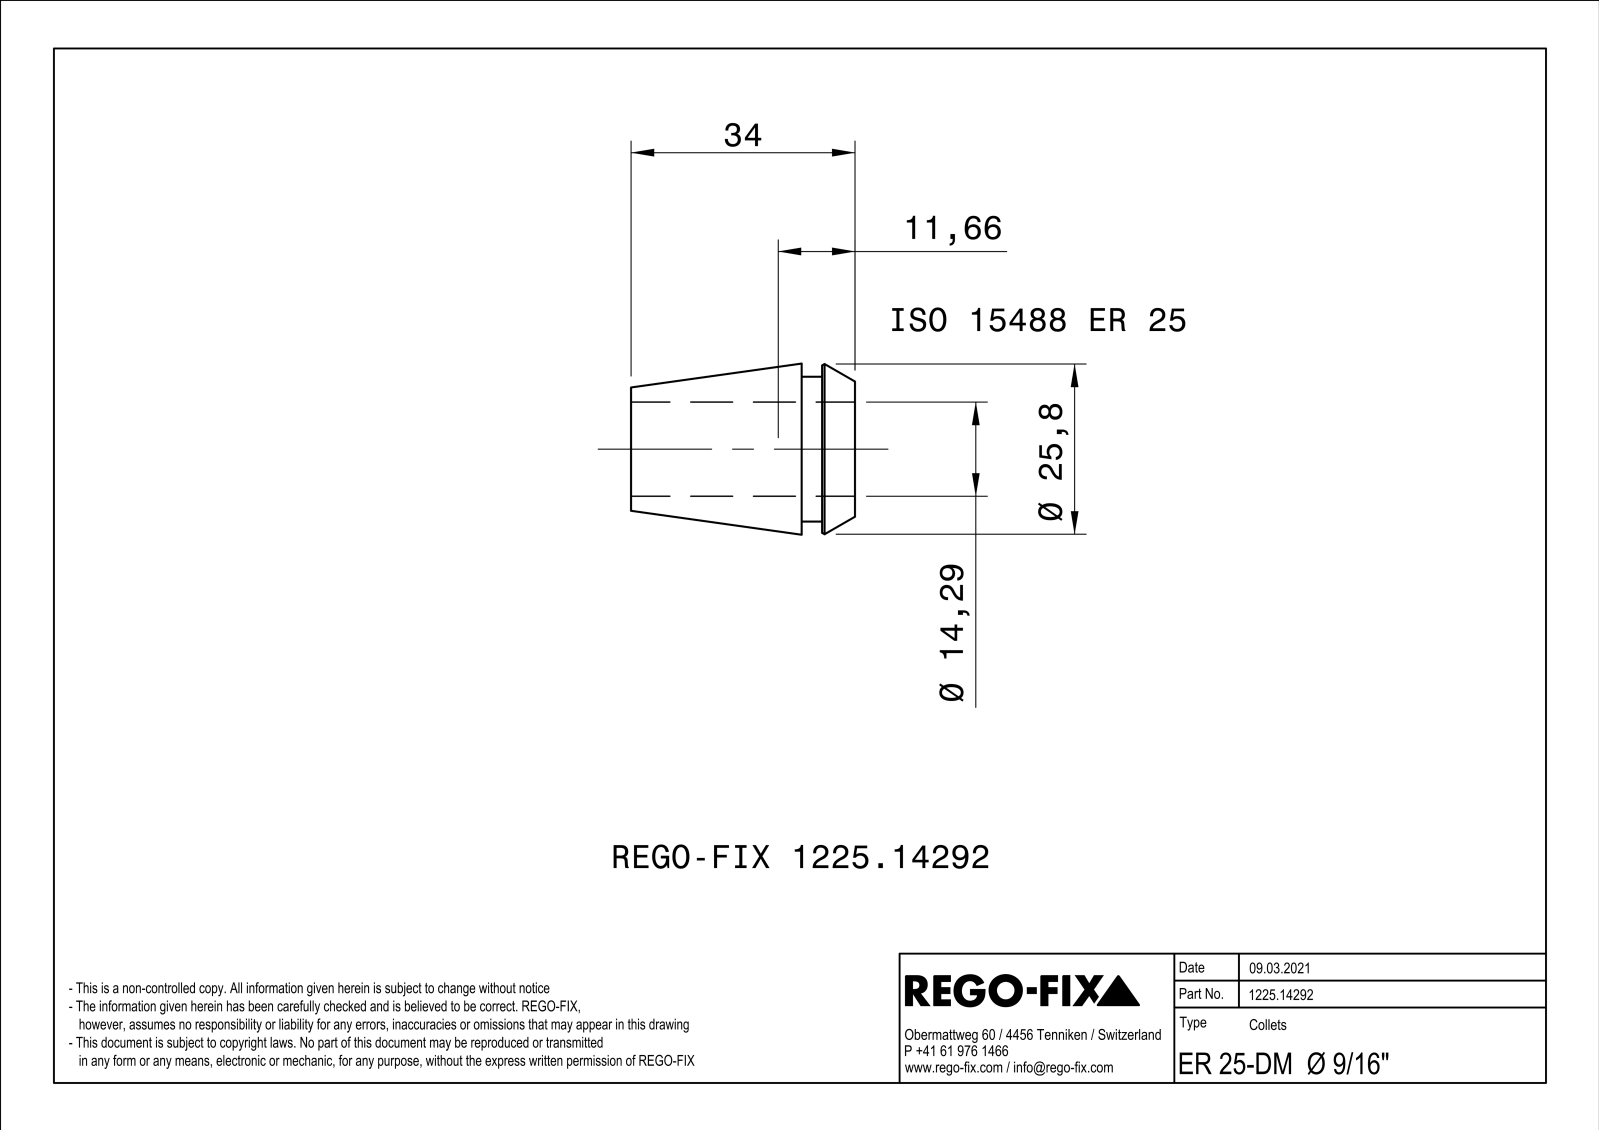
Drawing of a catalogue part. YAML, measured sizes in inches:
part_name: "NOCUT"
step_written_by: "SIEMENS PLM Software Solid Edge ST10 (AUTOMOTIVE_DESIGN)"
units: inches
bodies: {solids: 1, faces: 154, planar: 80, cylindrical: 9, other: 65}
overall_size: [1.339, 1.023, 1.023]
volume: 0.421
surface_area: 10.87
round_holes:
  - {diameter: 0.563, count: 1}
round_bosses_or_shafts:
  - {diameter: 0.866, count: 1}
face_to_face_distances: [0.031, 0.319, 0.197, 0.122, 1.142, 1.339, 1.02, 0.591, 0.394, 0.272]
